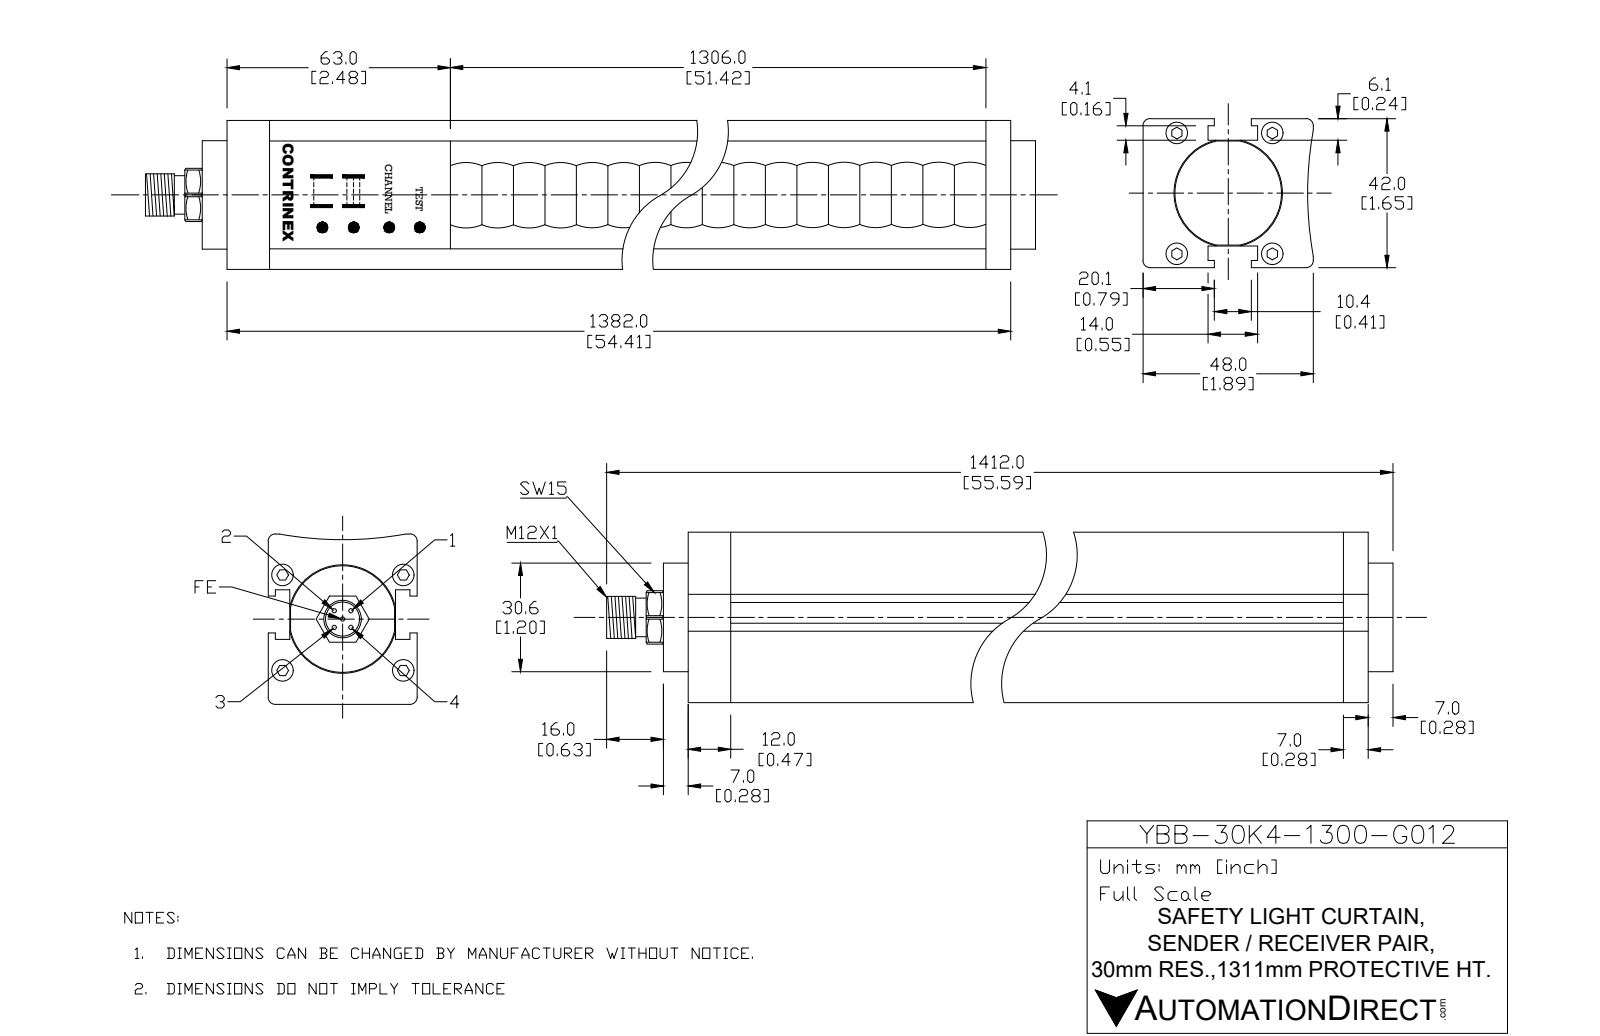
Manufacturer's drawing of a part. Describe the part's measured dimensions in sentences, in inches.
The part is named "YBB-30K4-1300-G012". Its 3-D file was written by "SolidWorks 2019 (AUTOMOTIVE_DESIGN)". It is 1 solid with 533 faces: 121 planar, 152 cylindrical and 260 other. Overall it measures 55.592 by 1.89 by 1.654 inches. Its volume is 141.9 cubic inches and its surface area 624.2 square inches. Round holes: 4 of diameter 0.12, 4 of diameter 0.236, 1 of diameter 0.335. Round bosses or shafts: 5 of diameter 0.039, 4 of diameter 0.217, 4 of diameter 0.119, 1 of diameter 1.205, 1 of diameter 0.472, 1 of diameter 0.413. Partial cylindrical surfaces (rounded edges, fillets, slot ends): 36 of radius 0.035, 12 of radius 0.039, 10 of radius 0.016, 2 of radius 0.217, 1 of radius 0.02, 1 of radius 0.02, 1 of radius 0.323, 1 of radius 0.689. The main face-to-face distances are 0.231, 1.422, 1.654, 1.191, 1.827, 2.172, 2.005, 0.2, 1.454, 0.031. The hole center spacings are 0.828, 0.88, 1.059, 1.339, 1.707.
